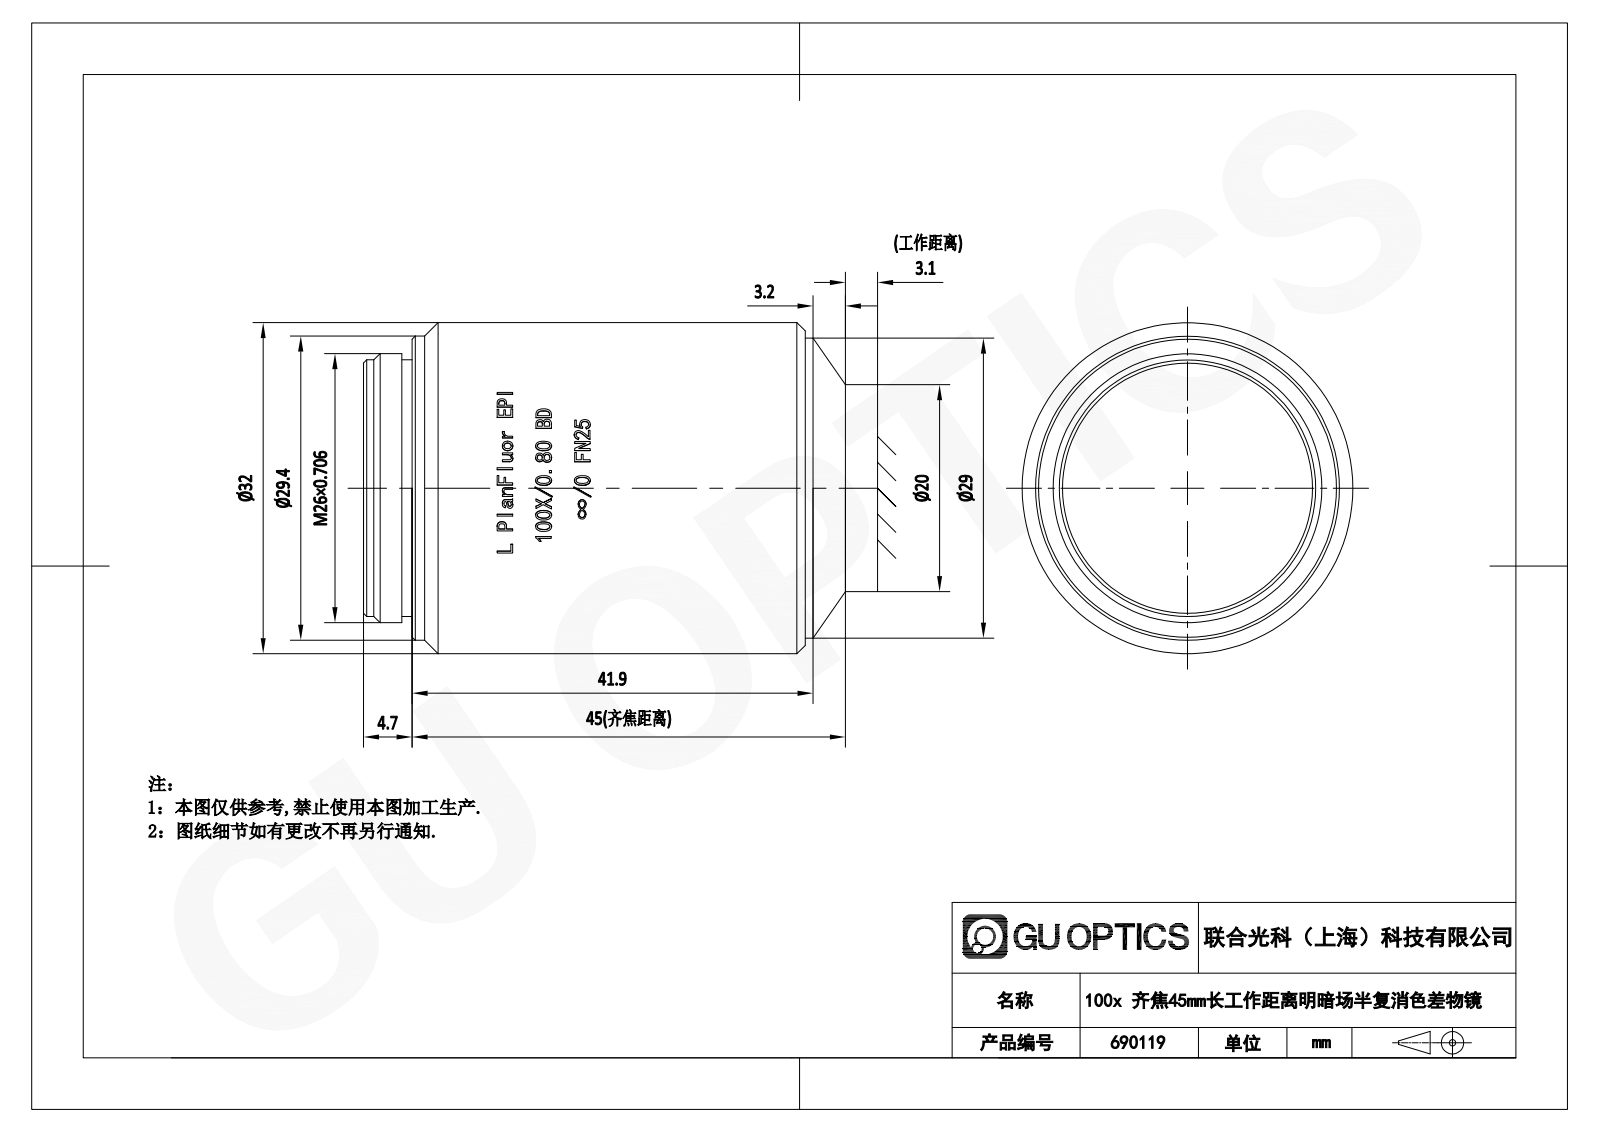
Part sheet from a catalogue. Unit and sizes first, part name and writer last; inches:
Units: inches
Overall size (bounding box): 1.835 × 1.262 × 1.26
Round bosses / shafts (diameter × count): ⌀1.26 ×1, ⌀1.157 ×1, ⌀1.142 ×1, ⌀1.024 ×1, ⌀0.976 ×1
Partial cylindrical surfaces — rounded edges, fillets, slot ends (radius × count): R0.632 ×1
Main face-to-face distances: 1.835, 0.185, 1.65, 1.681, 1.496, 0.154, 0.146, 0.039, 1.535, 1.689
Volume: 2.116 in³ · Surface area: 9.08 in²
Bodies: 1 solid, 349 faces (146 planar, 59 cylindrical, 144 other)
Part name (STEP PRODUCT): 690119
STEP written by: SolidWorks 2020 (CONFIG_CONTROL_DESIGN)
